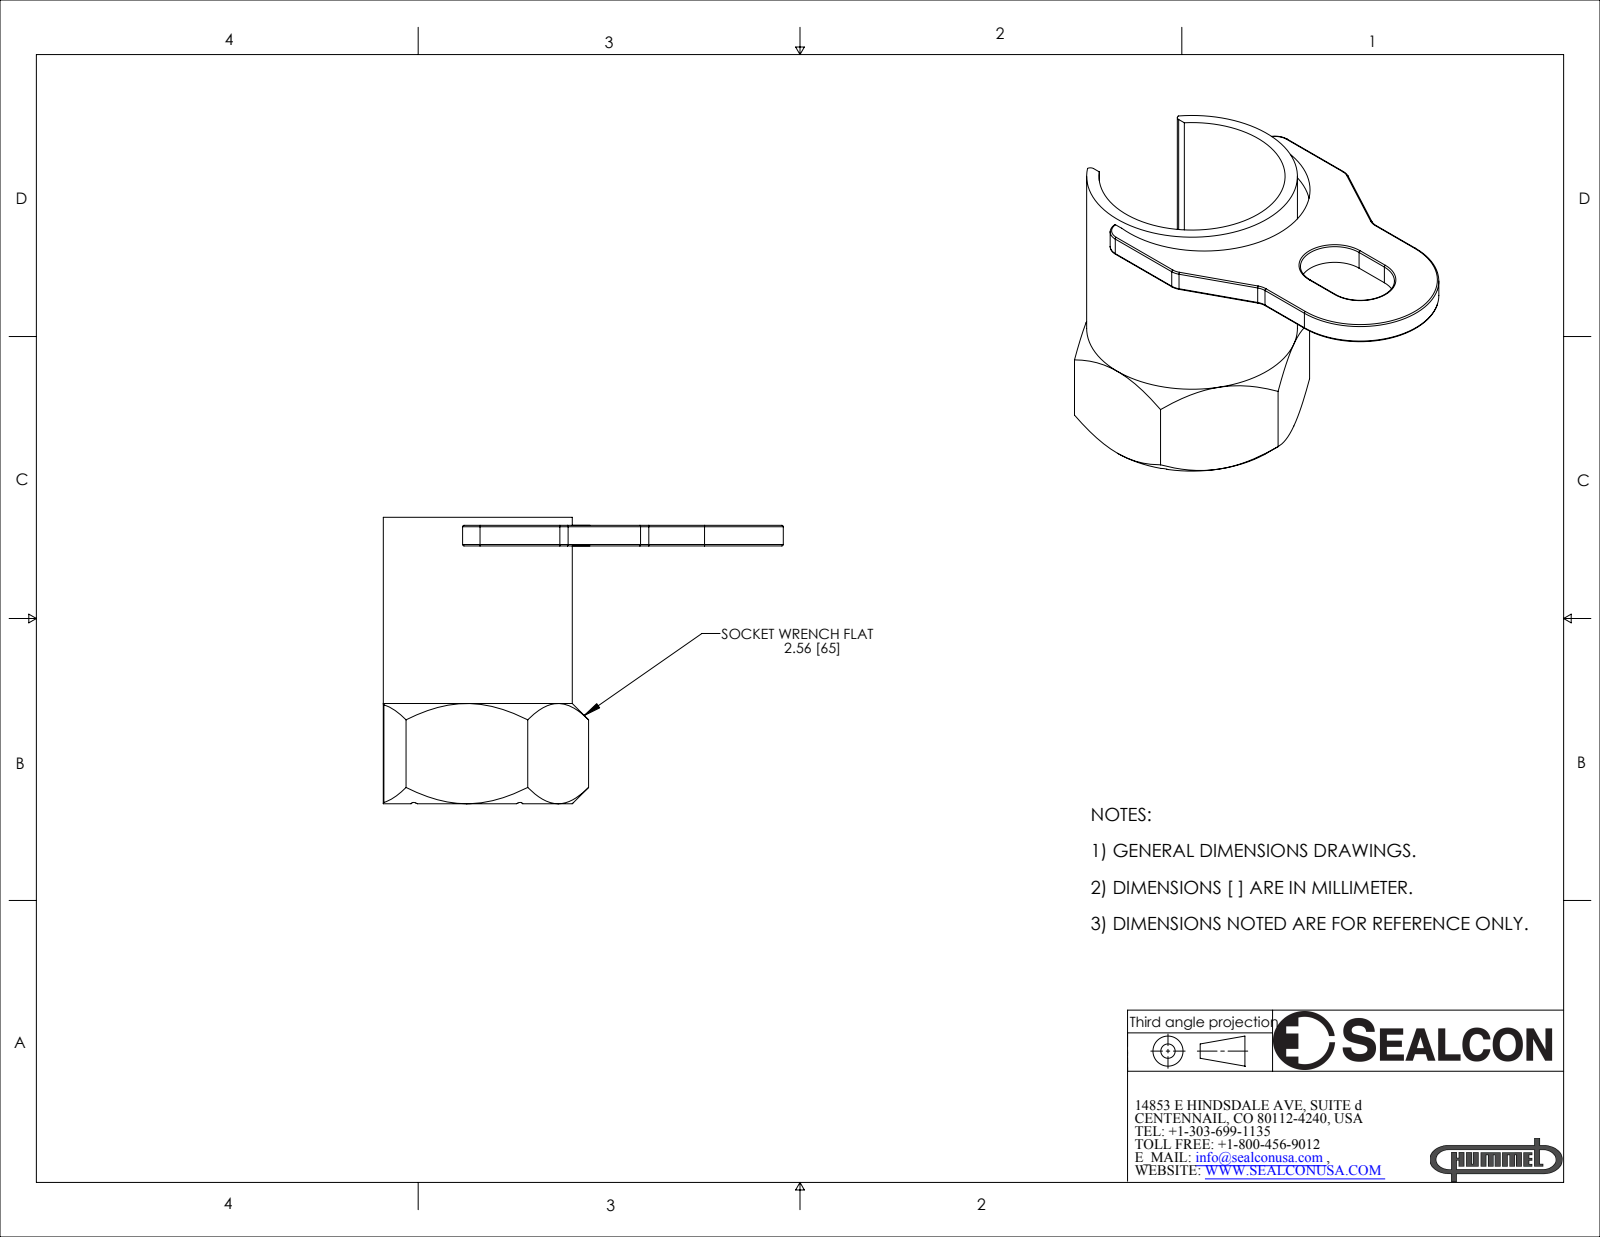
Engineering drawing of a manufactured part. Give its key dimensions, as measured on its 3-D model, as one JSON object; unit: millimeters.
{"part_name": "S-6500-WR", "step_written_by": "SolidWorks 2007 (CONFIG_CONTROL_DESIGN)", "units": "millimeters", "bodies": {"solids": 1, "faces": 97, "planar": 36, "cylindrical": 37, "other": 24}, "overall_size": [139.7, 100, 85], "volume_mm3": 104974, "surface_area_mm2": 49100, "partial_cylinders_radius": [[0.5, 14], [1.6, 7], [6.1, 6], [12, 2], [27.5, 1], [32.5, 1], [36.81, 1], [36.97, 1]], "face_to_face_distances": [4.31, 7.2, 69.31, 73.62, 65, 10, 4.3, 2.8, 15.81, 57.81]}
